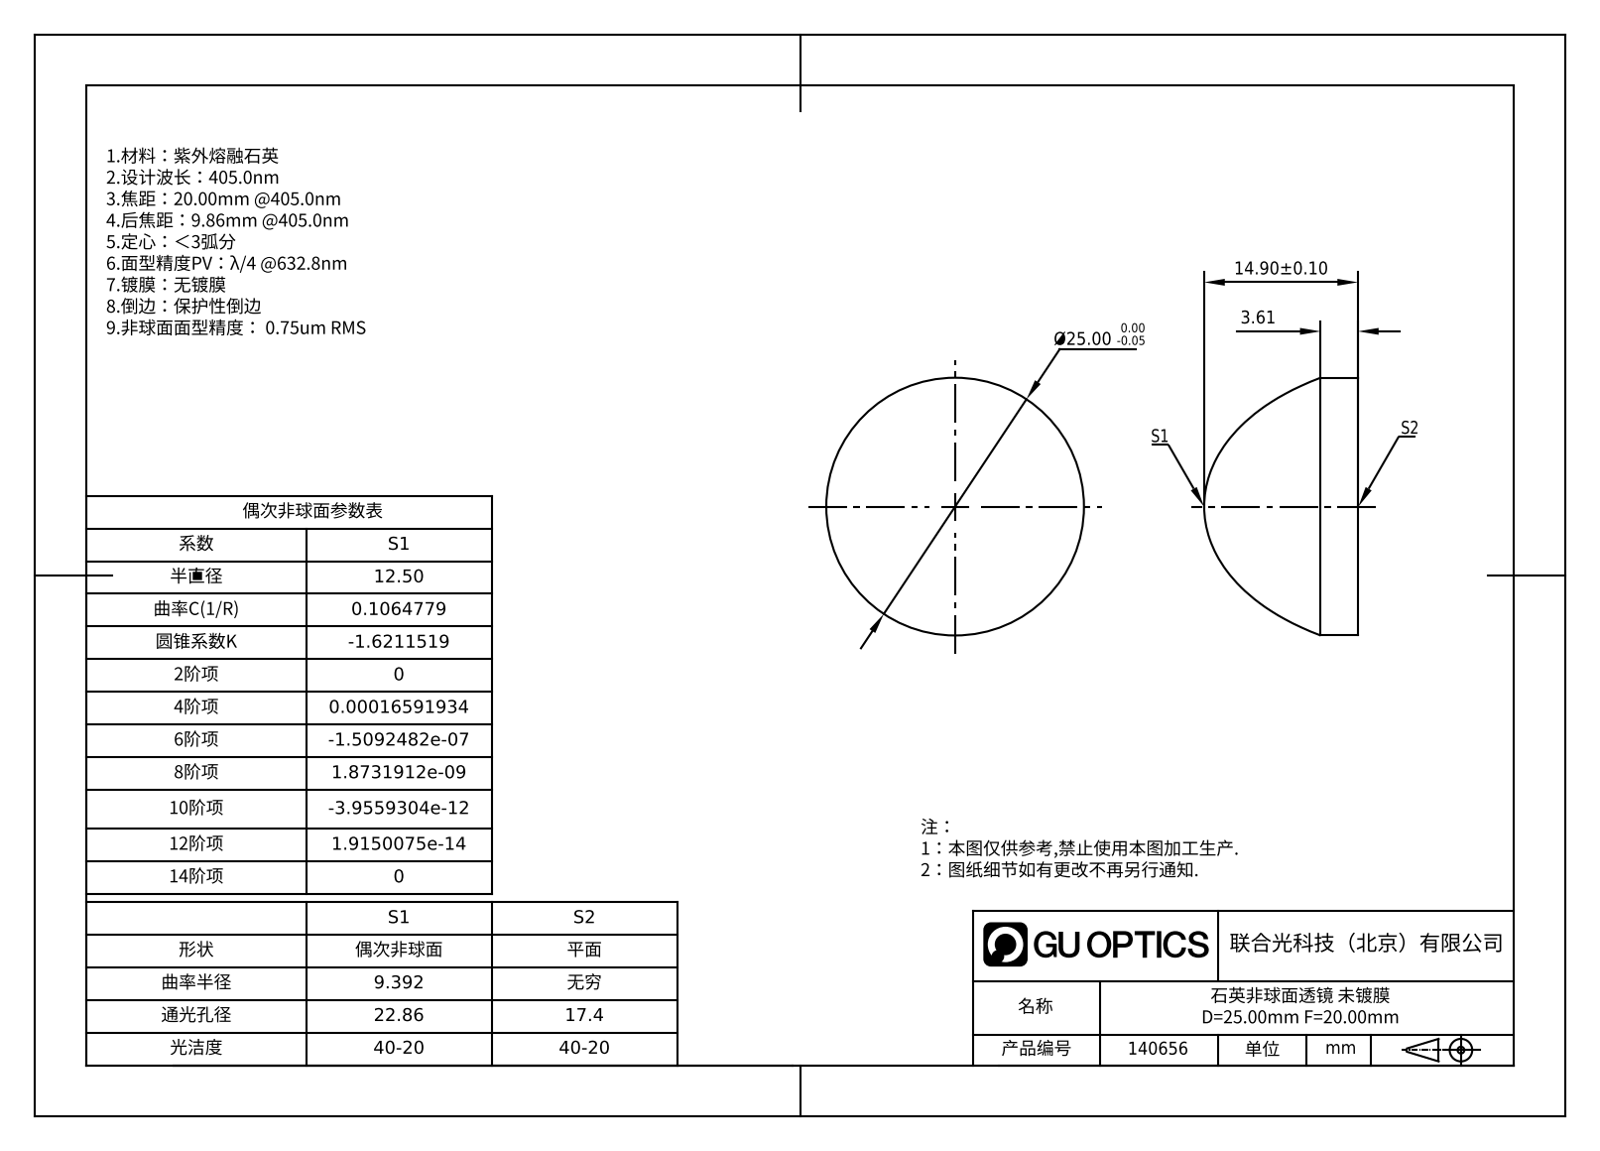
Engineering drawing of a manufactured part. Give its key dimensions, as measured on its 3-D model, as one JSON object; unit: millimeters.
{"part_name": "GASP21-025-020; surfaces 1,2.stp; GASP21-025-020.stp", "step_written_by": "SolidWorks 2023 (CONFIG_CONTROL_DESIGN)", "units": "millimeters", "bodies": {"solids": 1, "faces": 5, "planar": 1, "cylindrical": 2, "other": 2}, "overall_size": [25, 25, 14.9], "volume_mm3": 4854, "surface_area_mm2": 1599, "round_bosses_or_shafts": [[25, 1]]}
